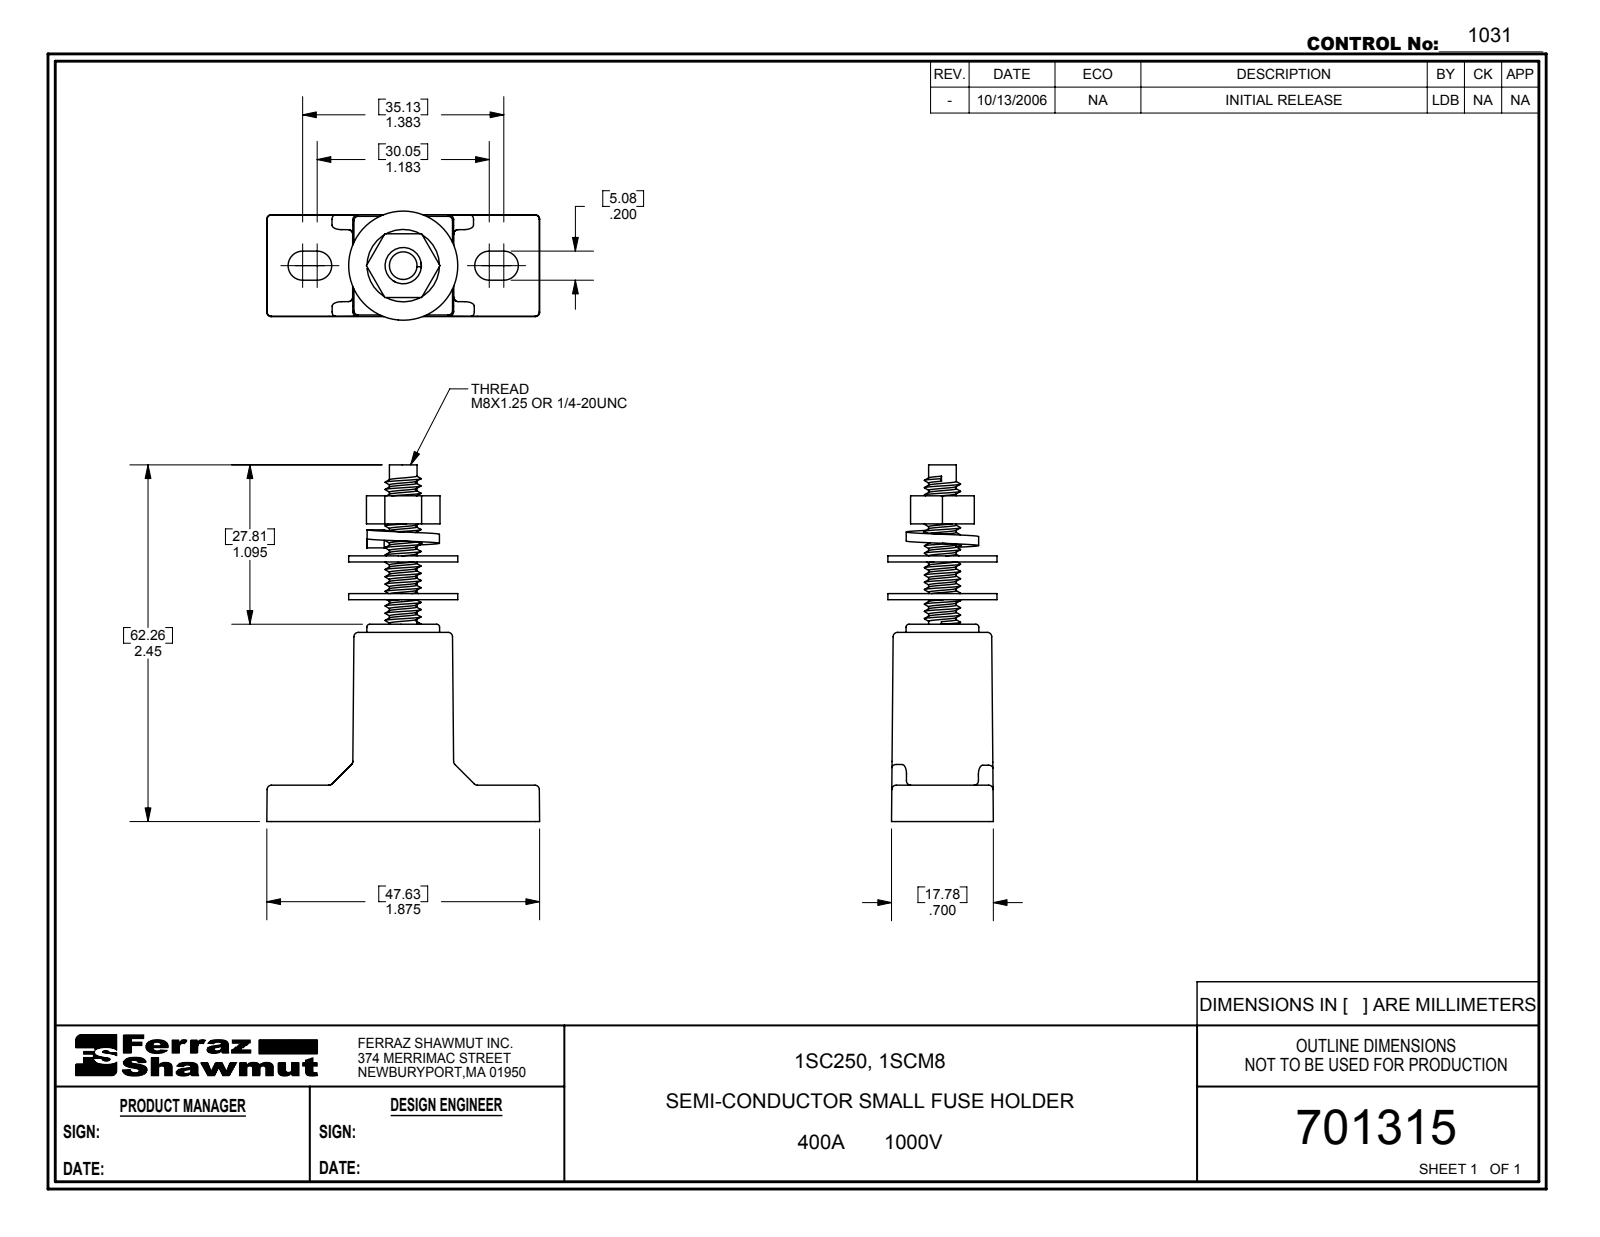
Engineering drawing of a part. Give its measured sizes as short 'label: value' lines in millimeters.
name: 701315rev
written by: SolidWorks 2016 (AUTOMOTIVE_DESIGN)
unit: mm
bodies: 0 solids, 246 faces (67 planar, 107 cylindrical, 72 other)
size: 62.3 × 47.6 × 19.1
holes: 1× ⌀7.1
bosses: 1× ⌀19.1, 1× ⌀12.7, 1× ⌀12.6, 1× ⌀4.8
rounds: 66× R0.8, 4× R2.5
face distances: 1.9, 9.5, 7.6, 6.4, 38.7, 39.8, 45.3, 46.4, 32.4, 33.4
